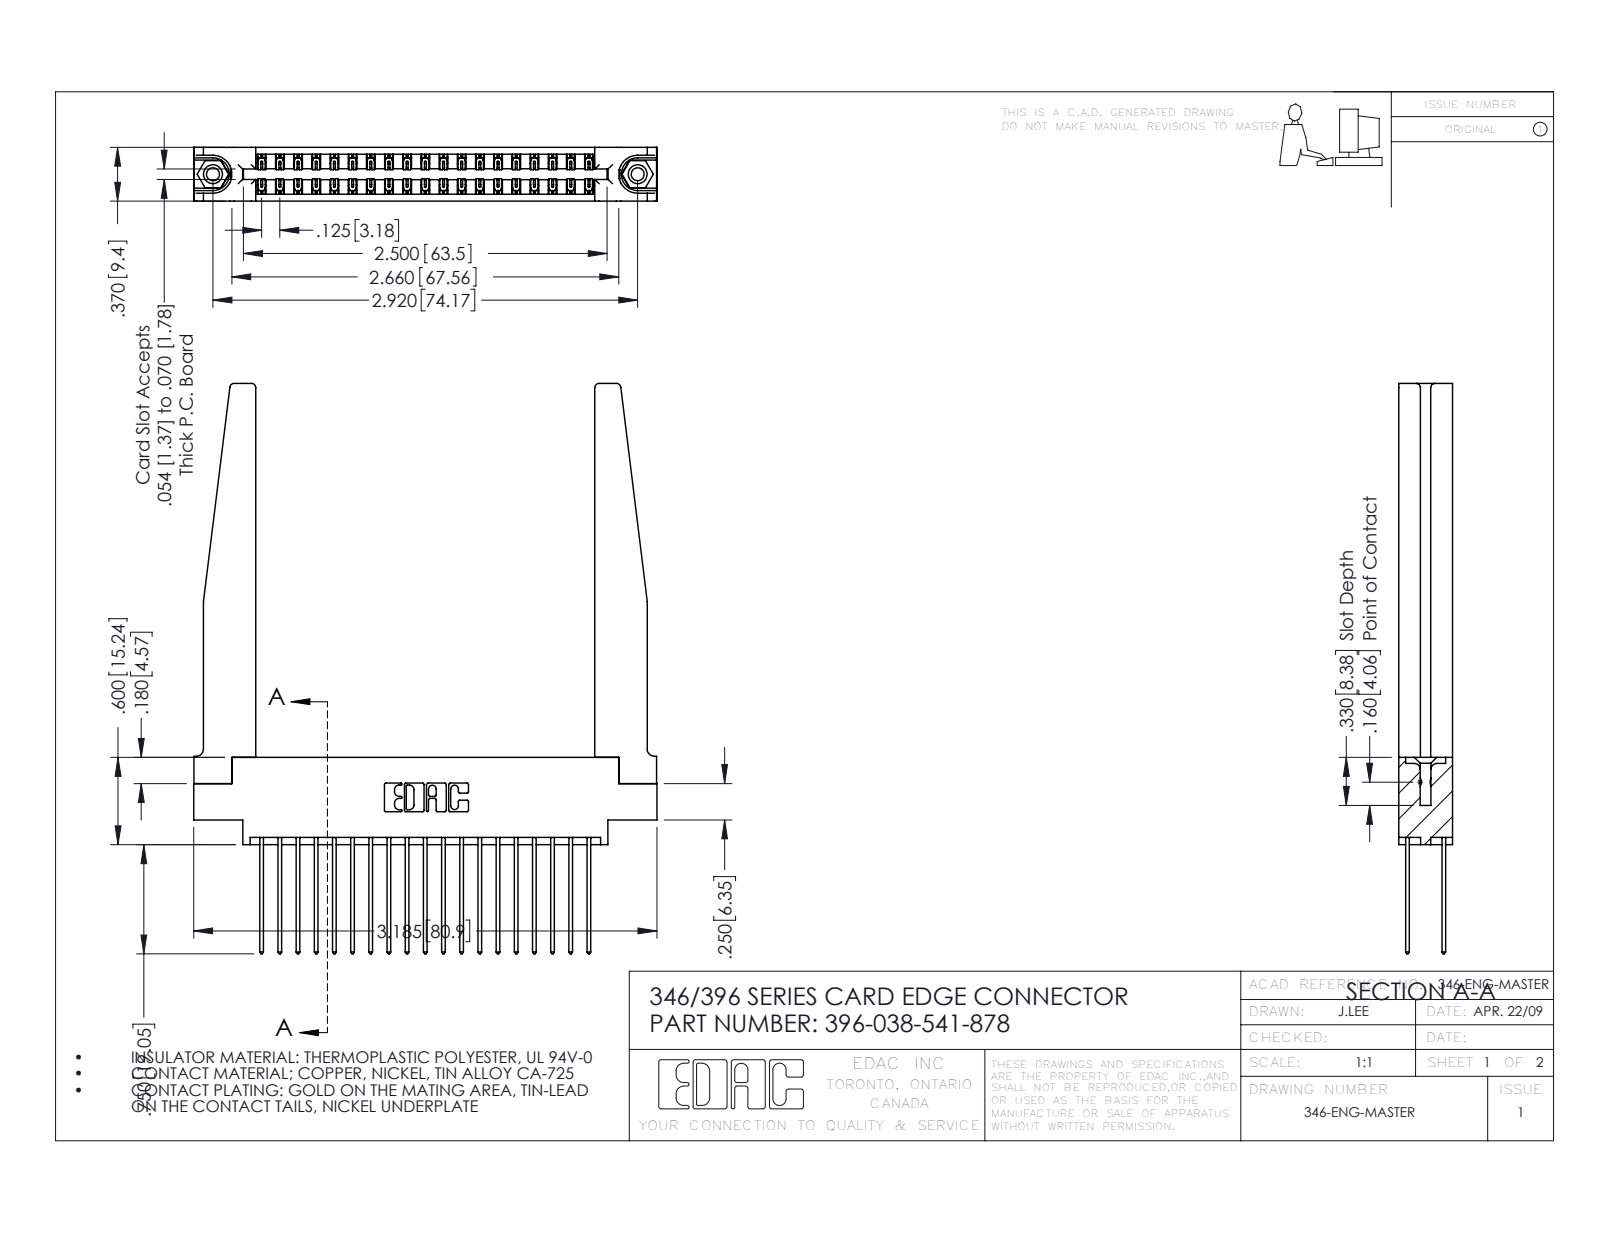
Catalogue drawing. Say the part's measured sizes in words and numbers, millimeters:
The part is named "346-220-078_345-220-078; 345-292-001_345-293-141; 396-038-541-878; 345-250-001_345-250-001-102 (+1 more)". Its 3-D file was written by "SolidWorks 2016 (CONFIG_CONTROL_DESIGN)". It is 43 solids with 2336 faces: 1552 planar, 732 cylindrical and 52 other. Overall it measures 99.6 by 80.9 by 9.4 millimeters. Its volume is 14 700 cubic millimeters and its surface area 18 080 square millimeters. Round holes: 2 of diameter 2.3, 2 of diameter 3.2, 2 of diameter 4, 1 of diameter 1.6. Round bosses or shafts: 2 of diameter 3.9. Partial cylindrical surfaces (rounded edges, fillets, slot ends): 57 of radius 0.2, 38 of radius 0.3, 22 of radius 0.3, 8 of radius 0.8, 6 of radius 0.2, 6 of radius 0.8, 3 of radius 0.7, 2 of radius 0.4. The main face-to-face distances are 9.4, 1.2, 8.2, 1.8, 6.4, 3.8, 3.8, 7.6, 0.6, 7. The hole center spacings are 6.2, 68.9, 74.2.
